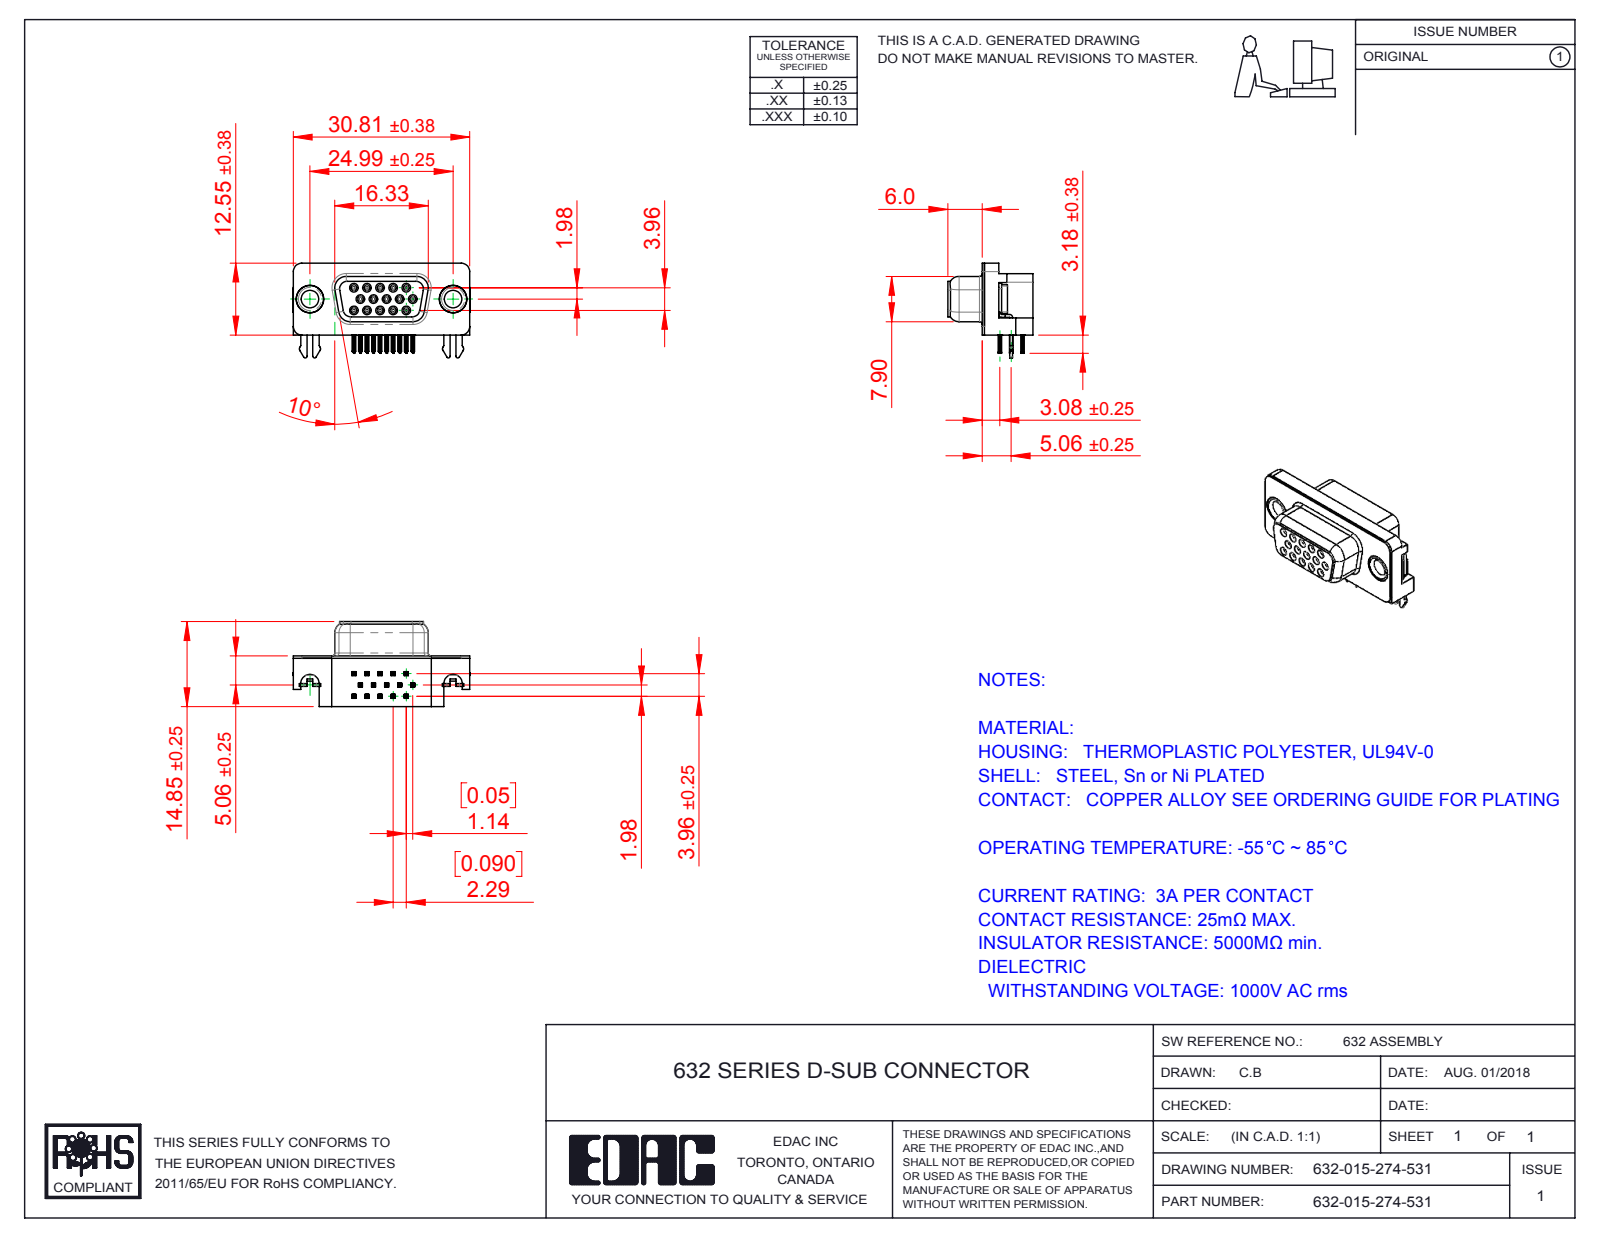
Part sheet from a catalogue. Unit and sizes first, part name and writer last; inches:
Units: inches
Overall size (bounding box): 1.216 × 0.652 × 0.585
Round holes (diameter × count): ⌀0.031 ×15, ⌀0.035 ×15, ⌀0.12 ×2, ⌀0.157 ×2, ⌀0.189 ×2, ⌀0.197 ×2
Round bosses / shafts (diameter × count): ⌀0.047 ×15, ⌀0.193 ×2, ⌀0.187 ×2, ⌀0.152 ×2
Partial cylindrical surfaces — rounded edges, fillets, slot ends (radius × count): R0.004 ×120, R0.006 ×60, R0.014 ×30, R0.013 ×15, R0.039 ×11, R0.011 ×10, R0.02 ×10, R0.01 ×8
Main face-to-face distances: 0.016, 0.078, 0.333, 0.348, 0.114, 0.098, 0.234, 0.252, 0.264, 0.278
Hole centre spacings: 0.09, 0.09, 0.156, 0.18, 0.238, 0.156, 0.18, 0.27
Volume: 0.177 in³ · Surface area: 7.736 in²
Bodies: 21 solids, 2298 faces (990 planar, 594 cylindrical, 714 other)
Part name (STEP PRODUCT): 632 Thru Hole Rivet; 632 Contact Middle_Recessed; 632 2 Prong Board Lock; 632 Housing_15 Socket (+5 more)
STEP written by: SolidWorks 2016 (CONFIG_CONTROL_DESIGN)
